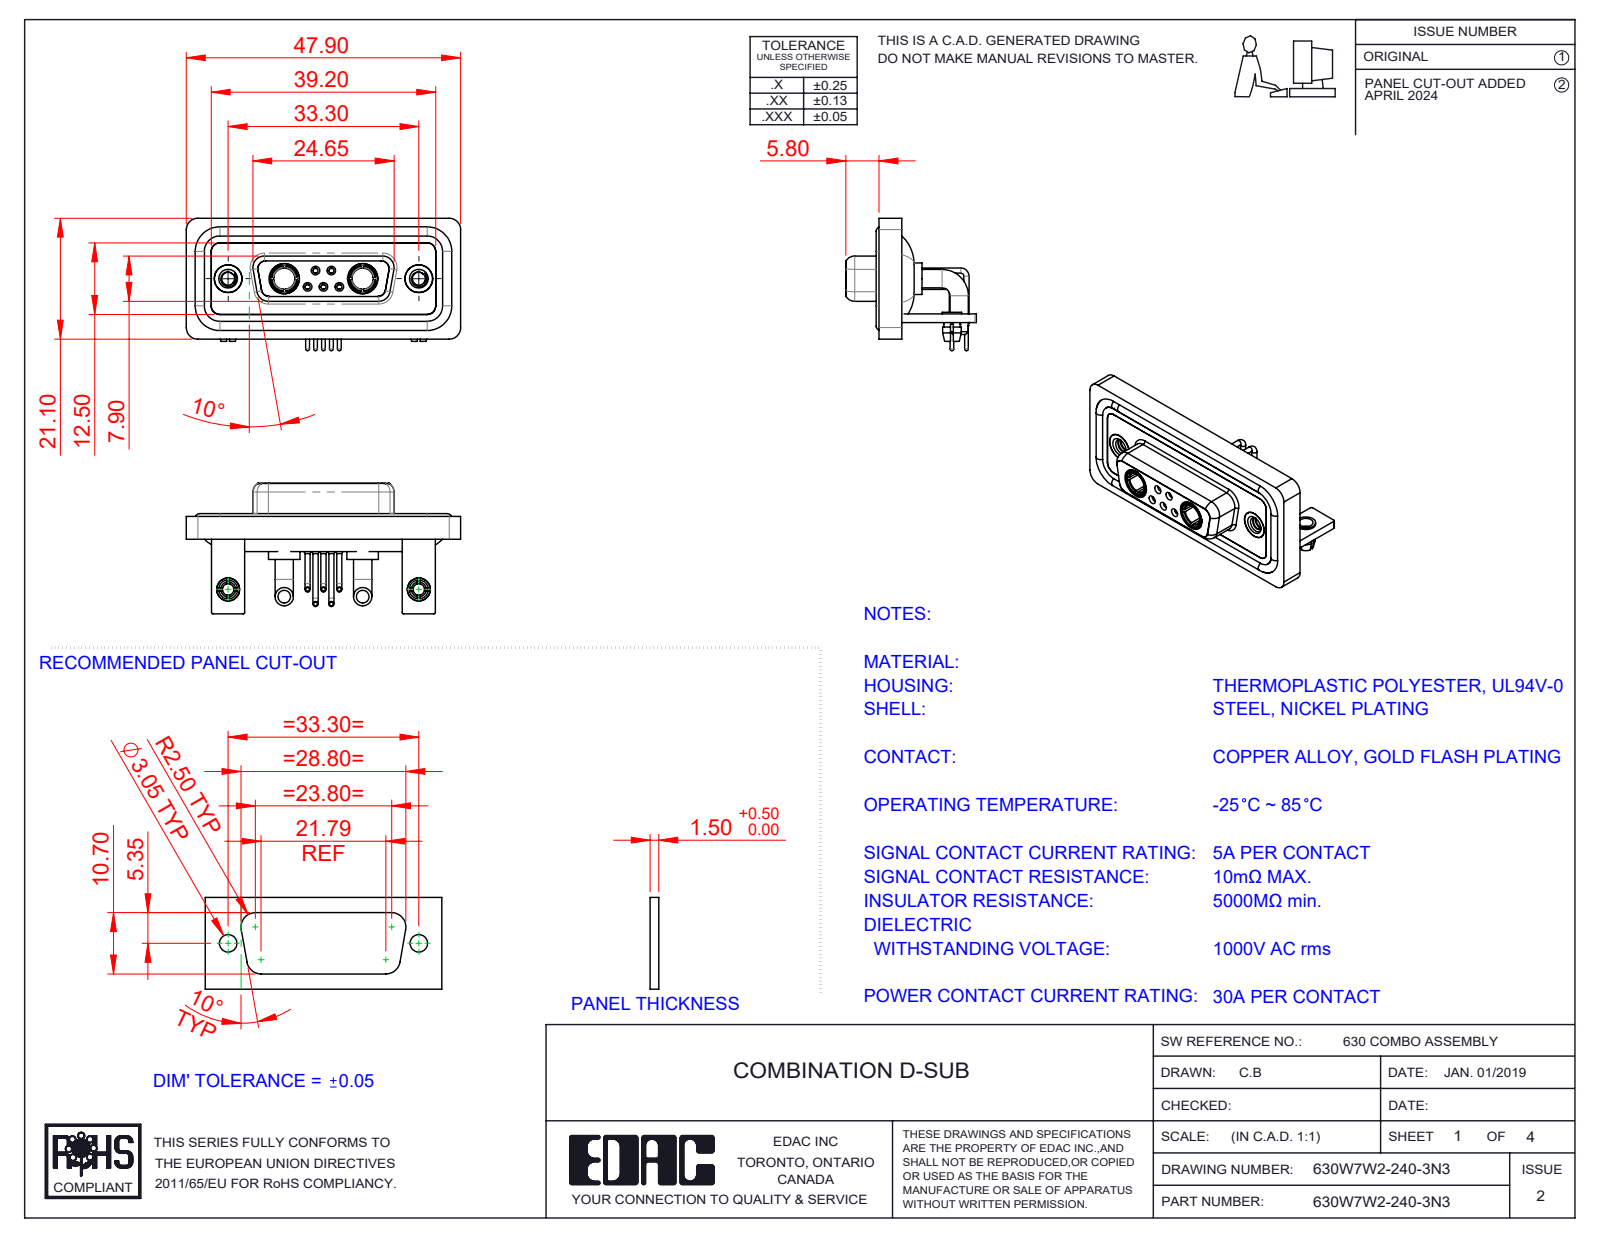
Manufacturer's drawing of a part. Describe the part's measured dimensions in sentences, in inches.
The part is named "630Combo Housing_7W2; 630Combo Shell Rear_15 Contacts; 630Combo Stabilizer Bracket_50 Contacts; 630W7W2-240-3N3 (+7 more)". Its 3-D file was written by "SolidWorks 2023 (CONFIG_CONTROL_DESIGN)". It is 20 solids with 947 faces: 306 planar, 409 cylindrical and 232 other. Overall it measures 1.886 by 0.91 by 0.898 inches. Its volume is 0.406 cubic inches and its surface area 17.34 square inches. Round holes: 7 of diameter 0.079, 5 of diameter 0.035, 5 of diameter 0.043, 5 of diameter 0.059, 4 of diameter 0.191, 3 of diameter 0.063, 2 of diameter 0.067, 2 of diameter 0.089, 2 of diameter 0.098, 2 of diameter 0.126, 2 of diameter 0.146, 2 of diameter 0.157. Round bosses or shafts: 6 of diameter 0.063, 5 of diameter 0.035, 5 of diameter 0.026, 4 of diameter 0.126, 2 of diameter 0.217, 2 of diameter 0.205, 2 of diameter 0.195, 2 of diameter 0.195. Partial cylindrical surfaces (rounded edges, fillets, slot ends): 21 of radius 0.079, 18 of radius 0.059, 16 of radius 0.01, 12 of radius 0.053, 8 of radius 0.063, 5 of radius 0.02, 4 of radius 0.024, 4 of radius 0.026. The main face-to-face distances are 0.016, 0.114, 0.059, 0.071, 0.146, 0.043, 0.161, 0.063, 0.098, 0.055. The hole center spacings are 0.124, 0.109, 0.386, 0.925, 1.311, 0.17, 0.17, 0.198.
